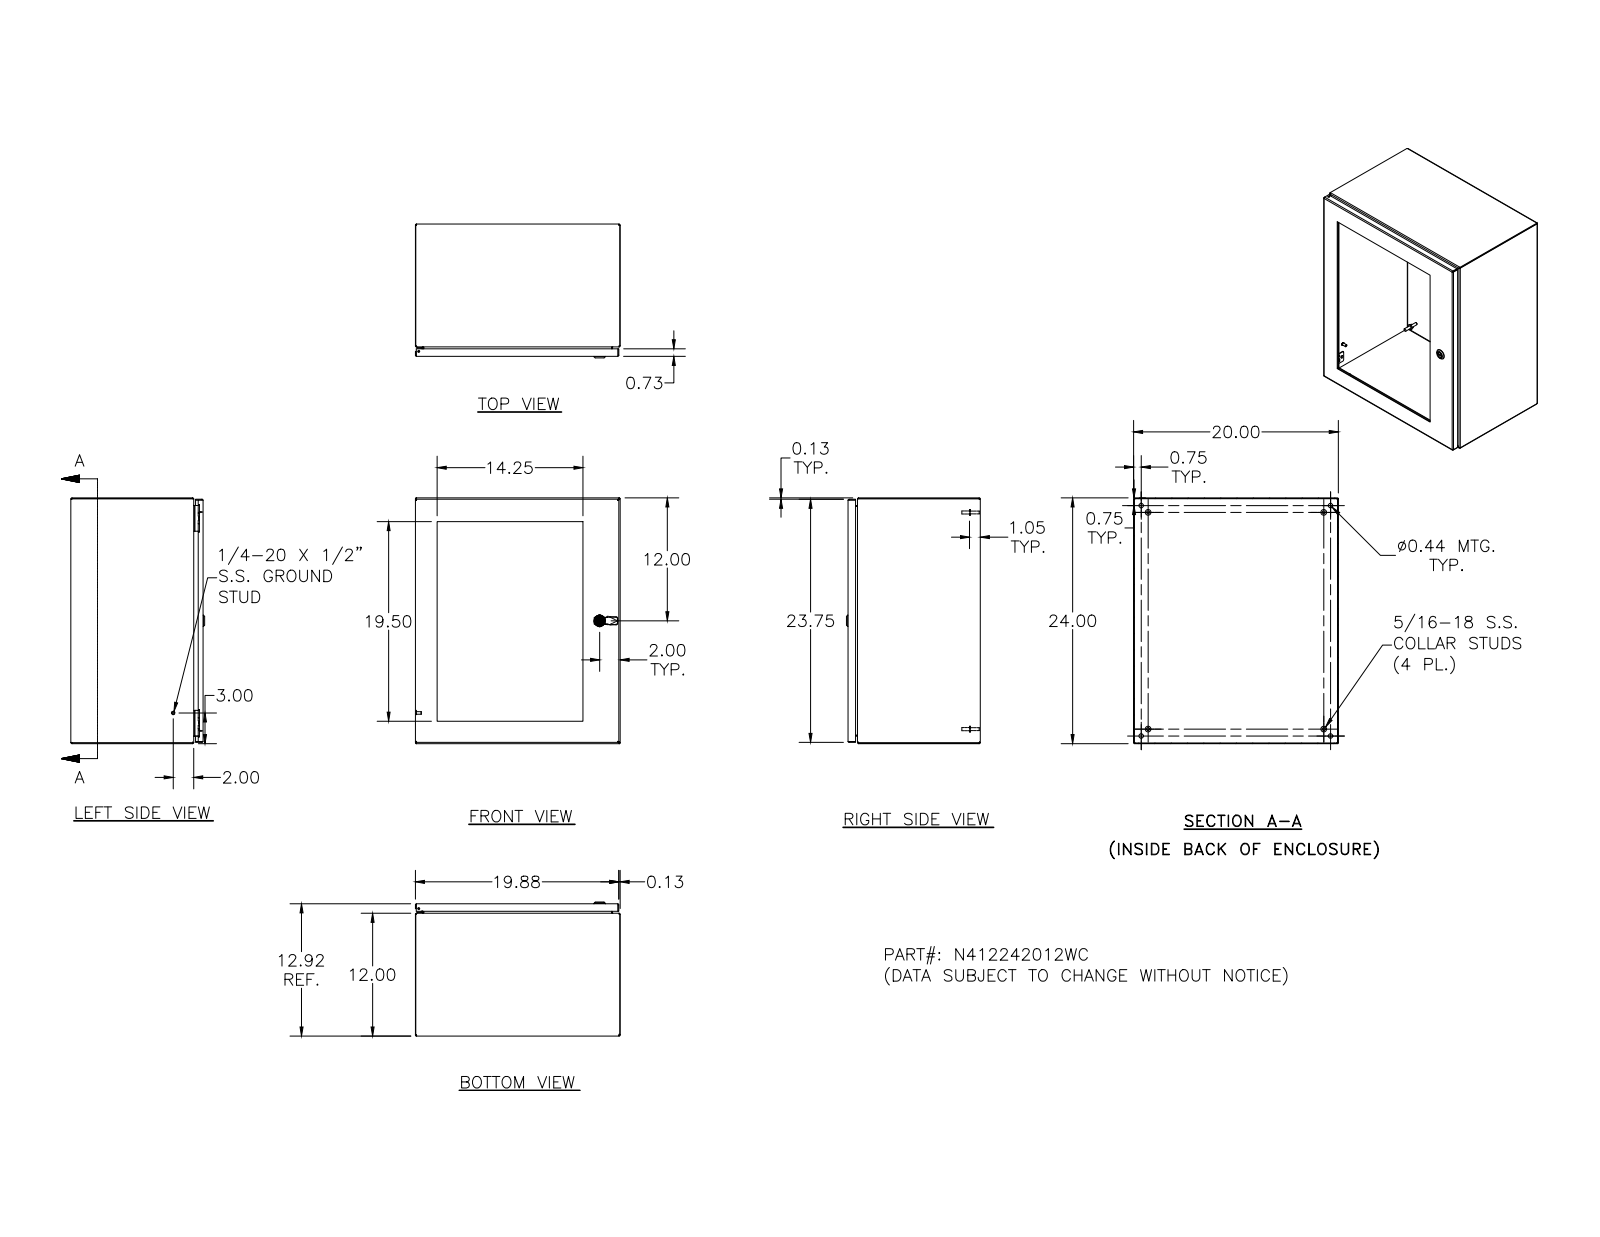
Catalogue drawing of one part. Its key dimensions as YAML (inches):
part_name: "N412242012WC"
step_written_by: "SolidWorks 2018 (AUTOMOTIVE_DESIGN)"
units: inches
bodies: {solids: 73, faces: 2083, planar: 775, cylindrical: 625, other: 683}
overall_size: [24, 20, 13.075]
volume: 225.8
surface_area: 4675
round_holes:
  - {diameter: 0.156, count: 20}
  - {diameter: 0.281, count: 18}
  - {diameter: 0.188, count: 5}
  - {diameter: 0.093, count: 4}
  - {diameter: 0.152, count: 4}
  - {diameter: 0.167, count: 4}
  - {diameter: 0.172, count: 4}
  - {diameter: 0.437, count: 4}
  - {diameter: 0.187, count: 1}
  - {diameter: 0.197, count: 1}
  - {diameter: 0.315, count: 1}
  - {diameter: 0.394, count: 1}
round_bosses_or_shafts:
  - {diameter: 0.337, count: 18}
  - {diameter: 0.19, count: 18}
  - {diameter: 0.25, count: 10}
  - {diameter: 0.563, count: 4}
  - {diameter: 0.36, count: 4}
  - {diameter: 0.32, count: 4}
  - {diameter: 0.3, count: 4}
  - {diameter: 0.275, count: 4}
partial_cylinders:
  - {radius: 0.031, count: 34}
  - {radius: 0.012, count: 30}
  - {radius: 0.05, count: 26}
  - {radius: 0.105, count: 24}
  - {radius: 0.016, count: 18}
  - {radius: 0.125, count: 16}
  - {radius: 0.02, count: 13}
  - {radius: 0.032, count: 8}
face_to_face_distances: [0.074, 12.843, 19.926, 12.769, 23.926, 0.25, 12.593, 12.519, 20, 19.852]
hole_center_spacings: [4, 8, 16.008, 12, 17.443, 20, 21.132, 15.5]
